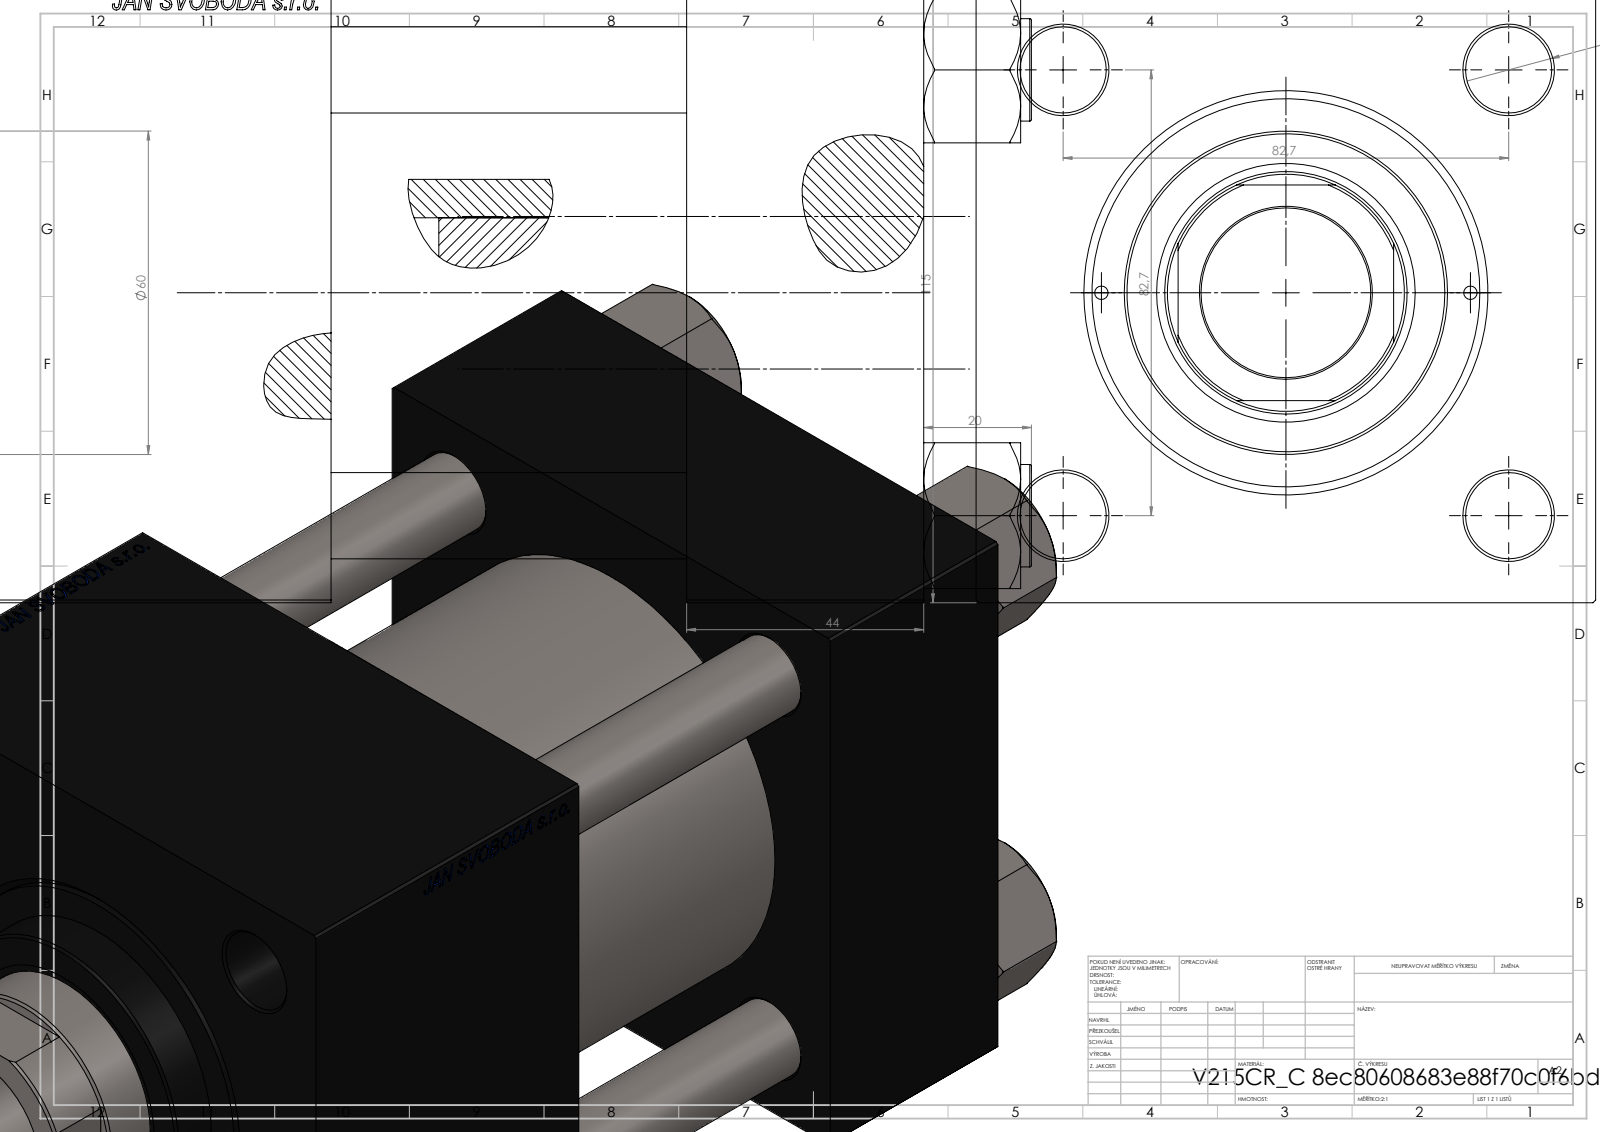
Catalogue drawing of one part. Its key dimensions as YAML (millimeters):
part_name: "V215_VC_A; V215CR_VCP_C; V215CR_C_Body; NUT_M5_C (+1 more)"
step_written_by: "SolidWorks 2019 (CONFIG_CONTROL_DESIGN)"
units: millimeters
bodies: {solids: 11, faces: 1202, planar: 576, cylindrical: 90, other: 536}
overall_size: [230, 115, 115]
volume: 1819000
surface_area: 273954
round_holes:
  - {diameter: 16, count: 4}
  - {diameter: 2.5, count: 2}
  - {diameter: 7, count: 2}
  - {diameter: 26.44, count: 2}
  - {diameter: 35, count: 2}
  - {diameter: 31.5, count: 1}
  - {diameter: 45, count: 1}
  - {diameter: 48, count: 1}
  - {diameter: 61, count: 1}
  - {diameter: 72, count: 1}
  - {diameter: 80, count: 1}
round_bosses_or_shafts:
  - {diameter: 19, count: 4}
  - {diameter: 86, count: 1}
  - {diameter: 60, count: 1}
partial_cylinders:
  - {radius: 22, count: 1}
face_to_face_distances: [115, 44, 110, 179, 135, 66, 69, 20, 150.3, 106.3]
hole_center_spacings: [41.96, 58.48, 82.7, 86.17, 34.25, 116.96, 68.5, 111]
